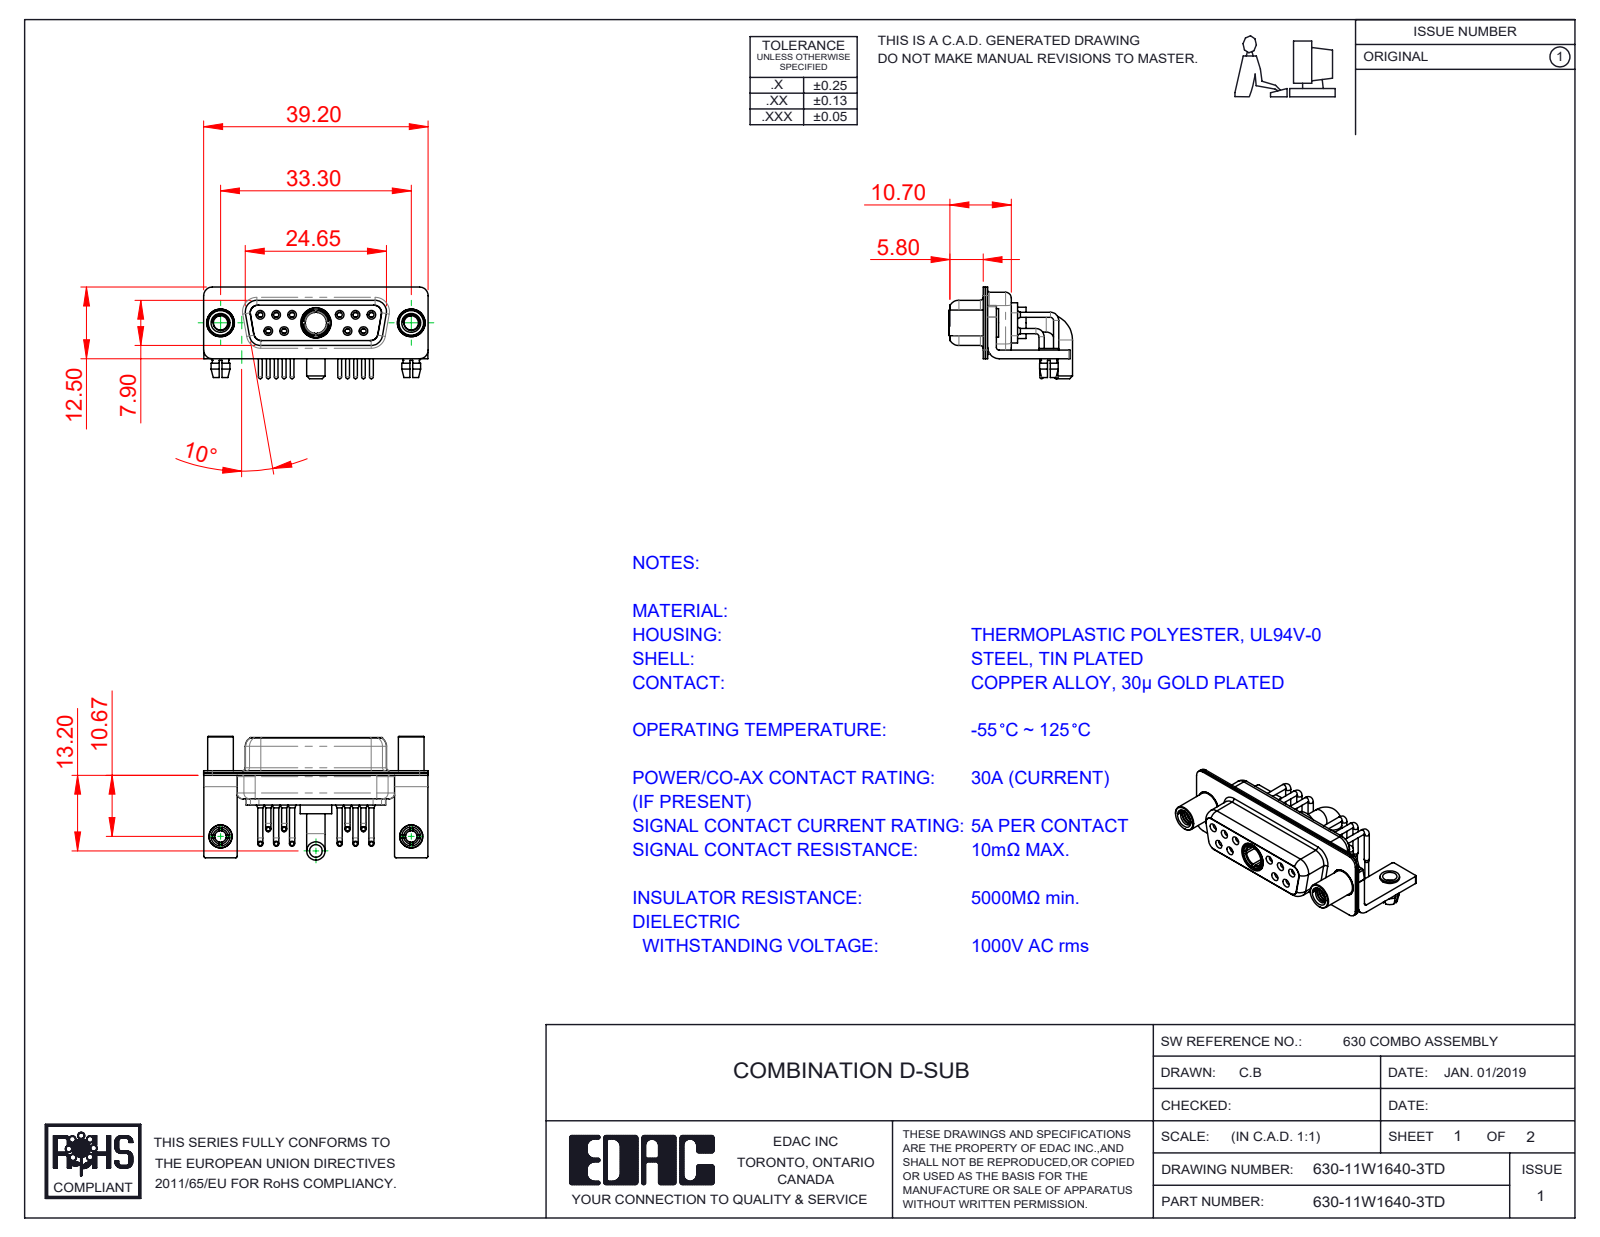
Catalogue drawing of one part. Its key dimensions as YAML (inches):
part_name: "630Combo Shell Rear_15 Contacts; 630Combo Threaded Standoff_D; Power Socket_30A RA; 630Combo Board Lock (+6 more)"
step_written_by: "SolidWorks 2020 (CONFIG_CONTROL_DESIGN)"
units: inches
bodies: {solids: 21, faces: 1077, planar: 316, cylindrical: 496, other: 265}
overall_size: [1.543, 0.85, 0.63]
volume: 0.189
surface_area: 11.51
round_holes:
  - {diameter: 0.079, count: 12}
  - {diameter: 0.035, count: 10}
  - {diameter: 0.043, count: 10}
  - {diameter: 0.059, count: 10}
  - {diameter: 0.067, count: 6}
  - {diameter: 0.063, count: 4}
  - {diameter: 0.098, count: 4}
  - {diameter: 0.191, count: 3}
  - {diameter: 0.126, count: 2}
  - {diameter: 0.157, count: 2}
  - {diameter: 0.159, count: 2}
  - {diameter: 0.146, count: 1}
round_bosses_or_shafts:
  - {diameter: 0.035, count: 10}
  - {diameter: 0.026, count: 10}
  - {diameter: 0.063, count: 6}
  - {diameter: 0.197, count: 2}
  - {diameter: 0.195, count: 2}
  - {diameter: 0.189, count: 2}
  - {diameter: 0.177, count: 2}
  - {diameter: 0.157, count: 2}
partial_cylinders:
  - {radius: 0.01, count: 16}
  - {radius: 0.059, count: 16}
  - {radius: 0.079, count: 13}
  - {radius: 0.053, count: 12}
  - {radius: 0.063, count: 8}
  - {radius: 0.02, count: 5}
  - {radius: 0.024, count: 4}
  - {radius: 0.026, count: 4}
face_to_face_distances: [0.016, 0.031, 0.018, 0.055, 0.333, 0.059, 0.071, 0.35, 0.244, 0.091]
hole_center_spacings: [0.124, 0.109, 0.545, 0.436, 0.654, 0.198, 0.198, 0.218]
